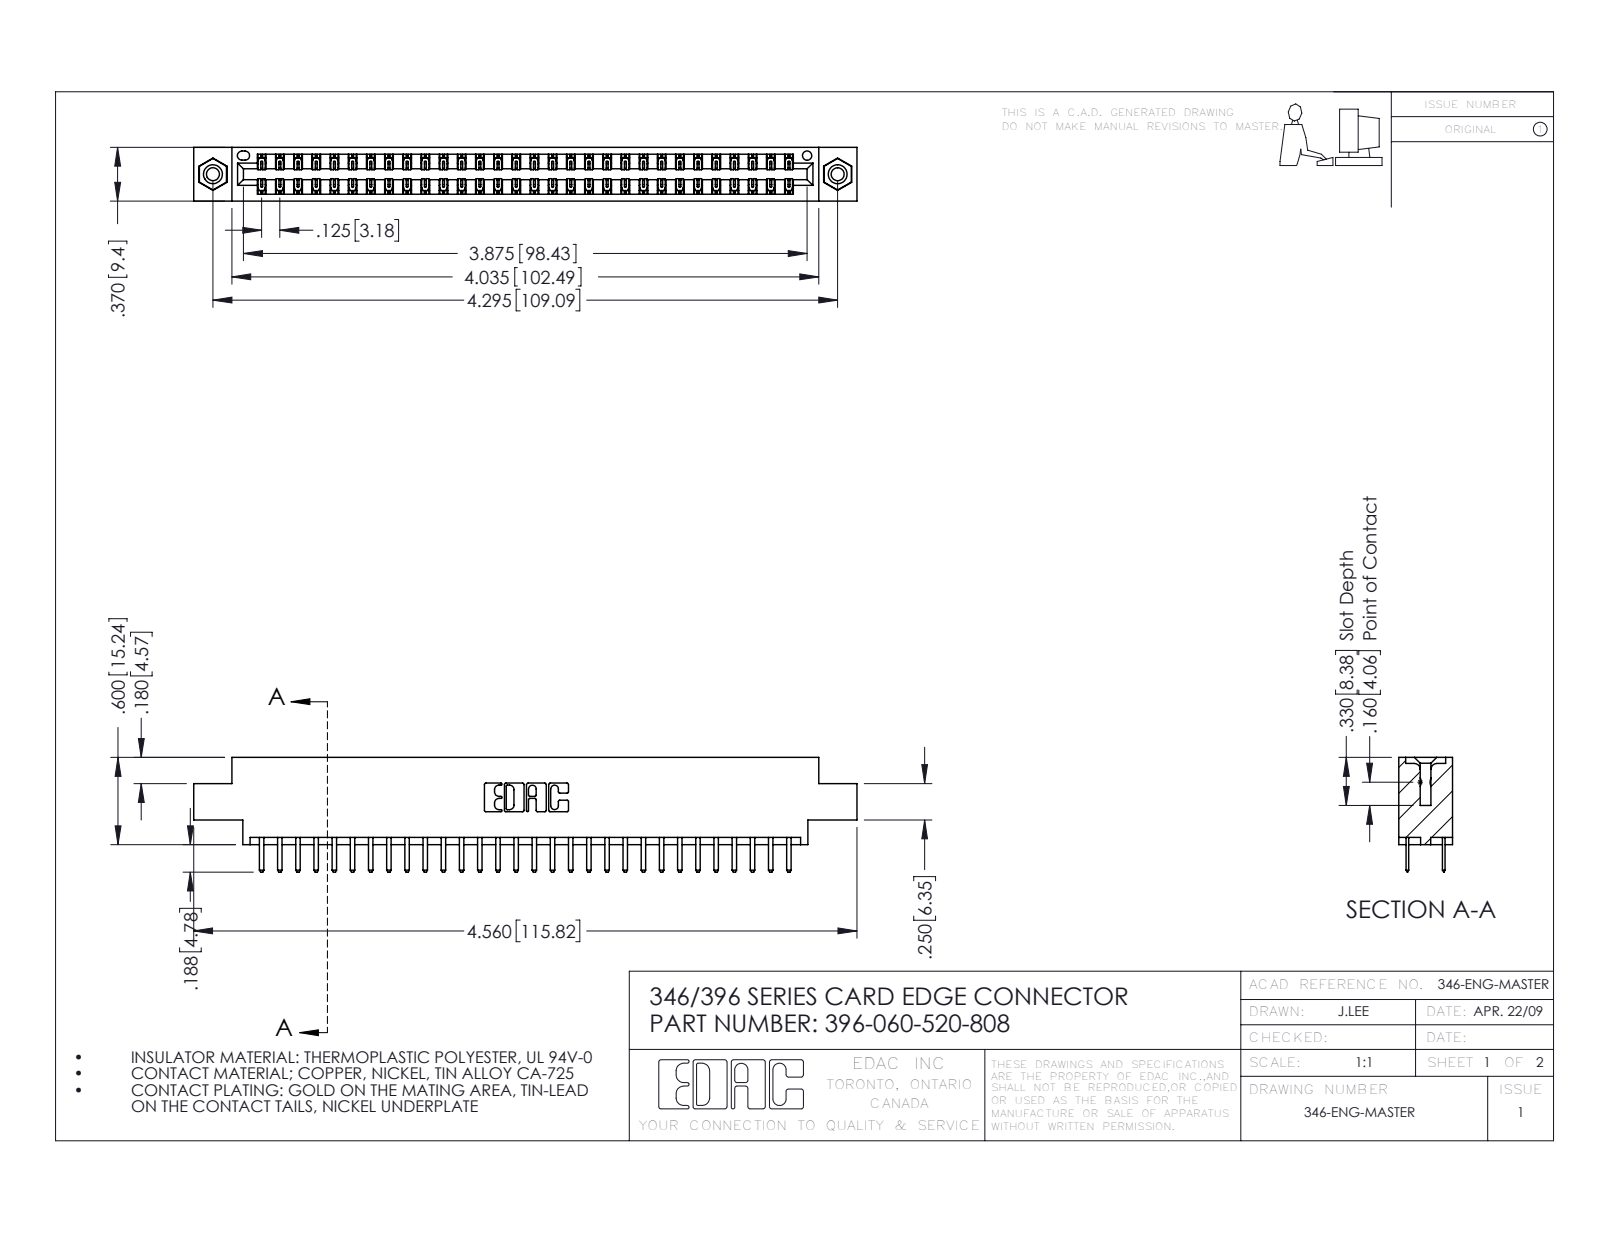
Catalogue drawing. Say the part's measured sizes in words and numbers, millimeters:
The part is named "346 Part_0.170 Offset - 0.156 Dia-TI; 345-292-001_345-293-120; 345-250-001_345-250-003-102; 396-060-520-808". Its 3-D file was written by "SolidWorks 2016 (CONFIG_CONTROL_DESIGN)". It is 63 solids with 3546 faces: 2332 planar, 1198 cylindrical and 16 other. Overall it measures 115.8 by 20 by 9.4 millimeters. Its volume is 11 000 cubic millimeters and its surface area 15 090 square millimeters. Round holes: 2 of diameter 2.3, 2 of diameter 3.2, 2 of diameter 4, 1 of diameter 1.6. Round bosses or shafts: 2 of diameter 3.9. Partial cylindrical surfaces (rounded edges, fillets, slot ends): 90 of radius 0.2, 64 of radius 0.3, 22 of radius 0.3, 6 of radius 0.2, 6 of radius 0.8, 3 of radius 0.7, 2 of radius 0.4, 2 of radius 0.6. The main face-to-face distances are 1.2, 8.2, 6.4, 9.4, 7, 1.8, 7.6, 0.6, 5.6, 3.8. The hole center spacings are 6.2, 103.8, 109.1.
